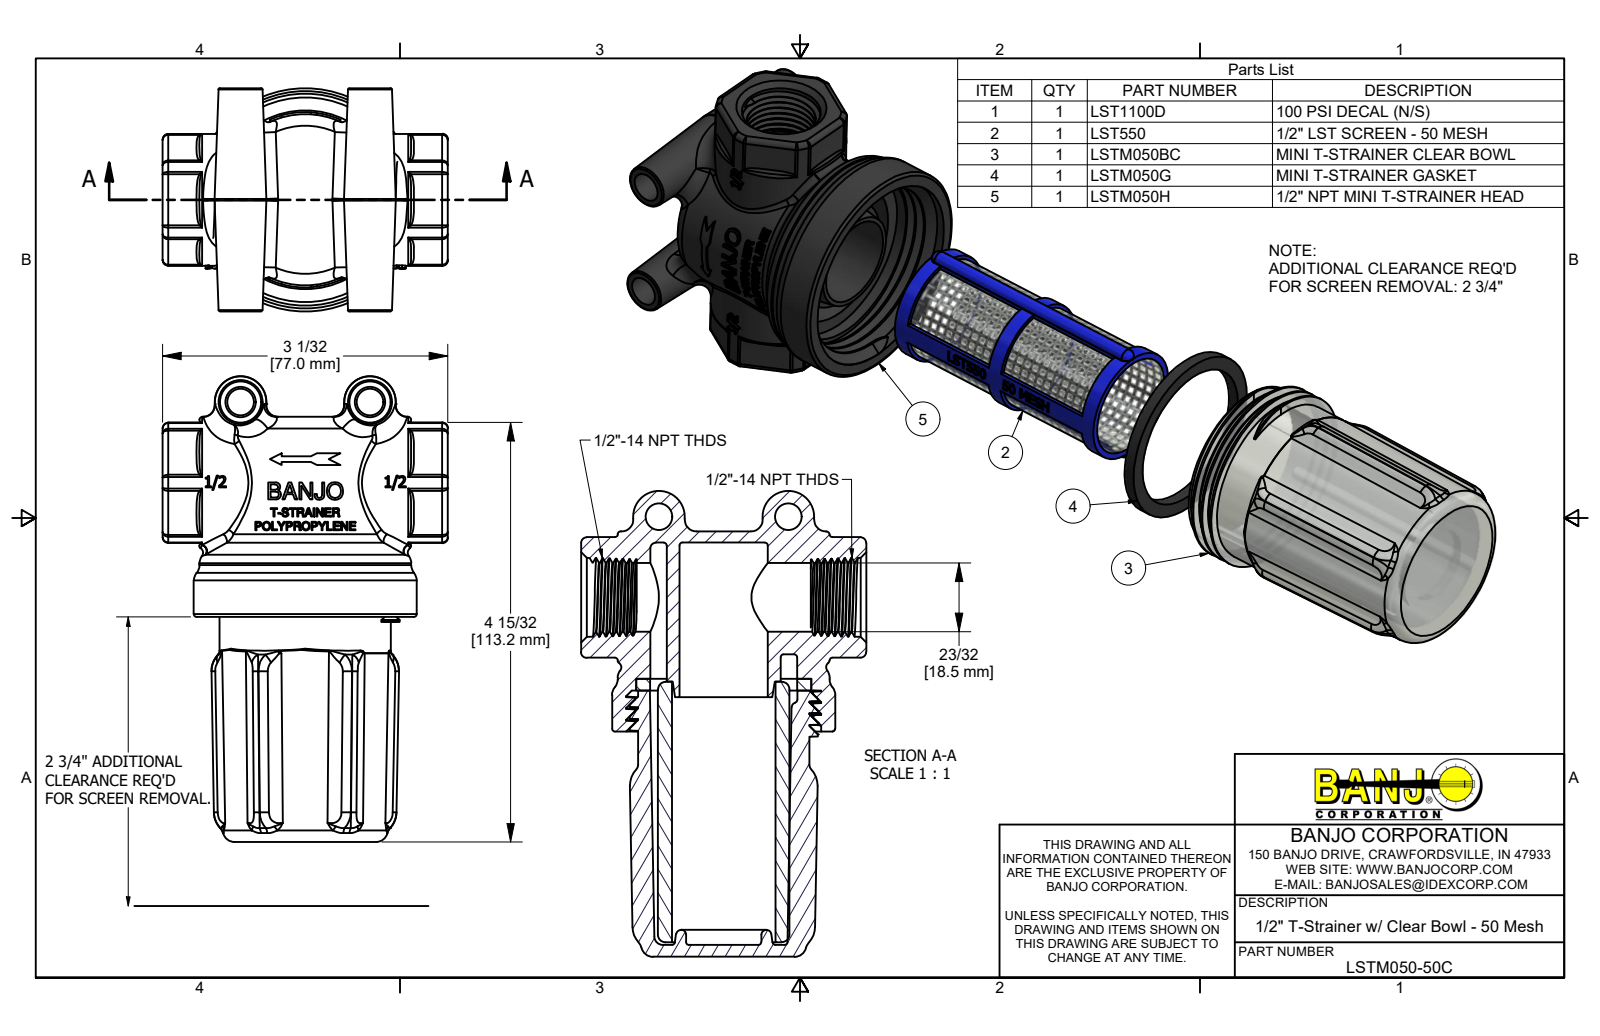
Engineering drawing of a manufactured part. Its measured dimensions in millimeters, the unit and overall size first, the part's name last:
Units: millimetres
Overall size (bounding box): 612.6 × 125.7 × 60.2
Round holes (diameter × count): ⌀18.5 ×1, ⌀20.3 ×1, ⌀23.8 ×1, ⌀28 ×1, ⌀39.6 ×1, ⌀39.7 ×1, ⌀48 ×1, ⌀52.7 ×1
Round bosses / shafts (diameter × count): ⌀60.2 ×1, ⌀57.2 ×1, ⌀50.8 ×1, ⌀47.3 ×1, ⌀47.2 ×1, ⌀46.2 ×1, ⌀35.6 ×1, ⌀31.2 ×1
Partial cylindrical surfaces — rounded edges, fillets, slot ends (radius × count): R1.5 ×24, R0.8 ×4, R2 ×4, R1.3 ×3, R2.1 ×2, R6.6 ×1, R13.9 ×1, R14.6 ×1
Main face-to-face distances: 71.8, 74.9, 3.2, 32.5, 114.7, 42.9, 39.8, 111.7, 39.9, 36.8
Volume: 133 600 mm³ · Surface area: 123 000 mm²
Bodies: 4 solids, 1373 faces (557 planar, 189 cylindrical, 627 other)
Part name (STEP PRODUCT): LSTM050-50C; LSTM050H; LSTM050G; LST550 (+1 more)
STEP written by: Autodesk Inventor 2019 (AUTOMOTIVE_DESIGN)
